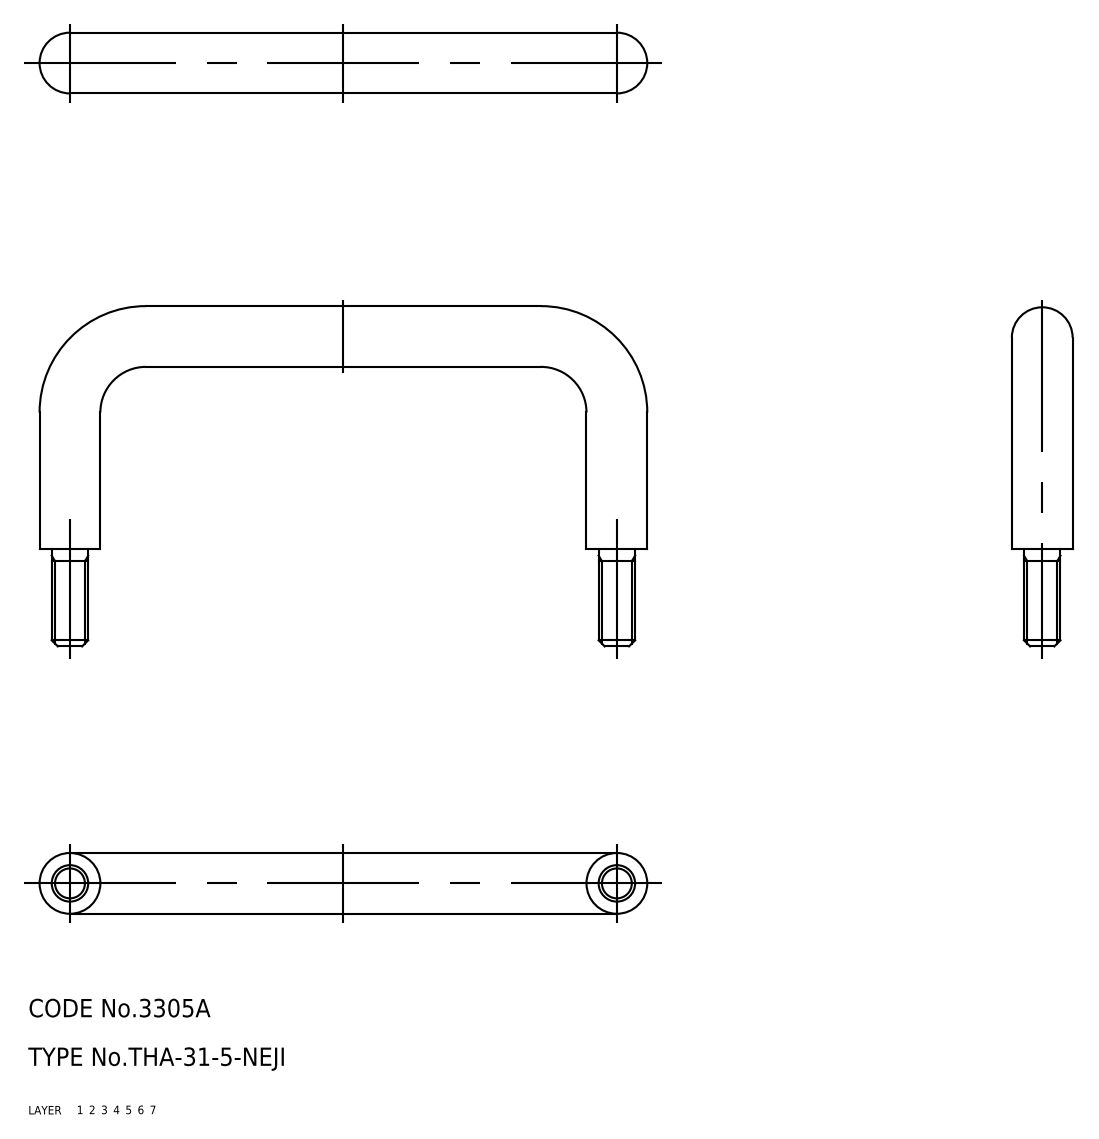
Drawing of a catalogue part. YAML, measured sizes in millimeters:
part_name: "pull"
step_written_by: "CADfix (AUTOMOTIVE_DESIGN)"
units: millimeters
bodies: {solids: 1, faces: 22, planar: 0, cylindrical: 0, other: 22}
overall_size: [100, 56, 10]
volume: 12654
surface_area: 5427
